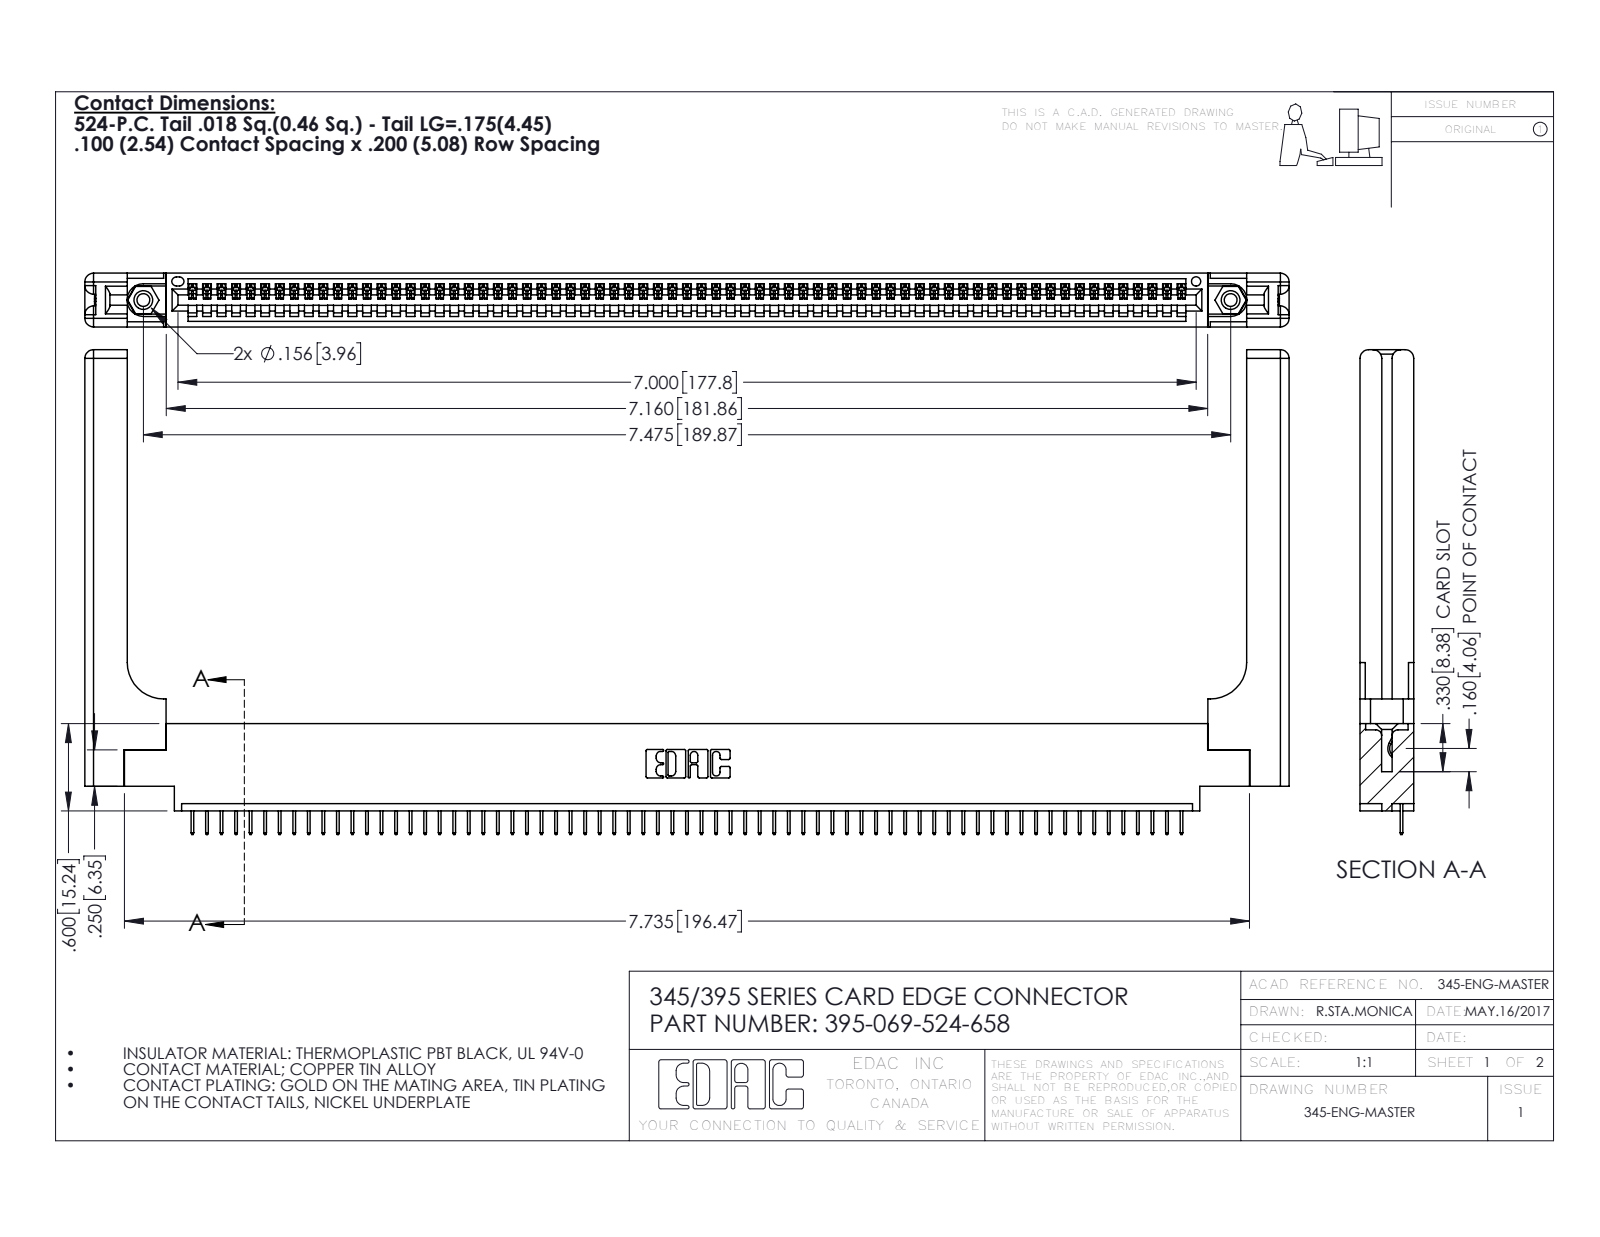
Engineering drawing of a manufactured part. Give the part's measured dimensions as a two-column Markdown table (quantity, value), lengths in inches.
| quantity | value |
| --- | --- |
| part name | 345-292-001_345-293-124; 395-069-524-658; 345 Part_0.170 Offset - 0.156 Dia-TH; 345-250-001_345-250-001-102 (+1 more) |
| STEP written by | SolidWorks 2016 (CONFIG_CONTROL_DESIGN) |
| units | inches |
| bodies | 74 solids, 4664 faces (3406 planar, 1198 cylindrical, 60 other) |
| overall size | 8.279 × 3.332 × 0.37 |
| volume | 1.728 in³ |
| surface area | 48.44 in² |
| round holes (diameter × count) | 0.089 × 2, 0.125 × 2, 0.156 × 2, 0.064 × 1 |
| round bosses / shafts (diameter × count) | 0.155 × 2 |
| partial cylindrical surfaces (radius × count) | 0.006 × 138, 0.01 × 22, 0.06 × 16, 0.007 × 6, 0.031 × 6, 0.026 × 3, 0.03 × 2, 0.031 × 2 |
| main face-to-face distances | 0.37, 0.072, 0.298, 0.098, 0.272, 0.025, 0.2, 0.225, 0.148, 0.15 |
| hole center spacings | 0.27, 7.239, 7.475 |
